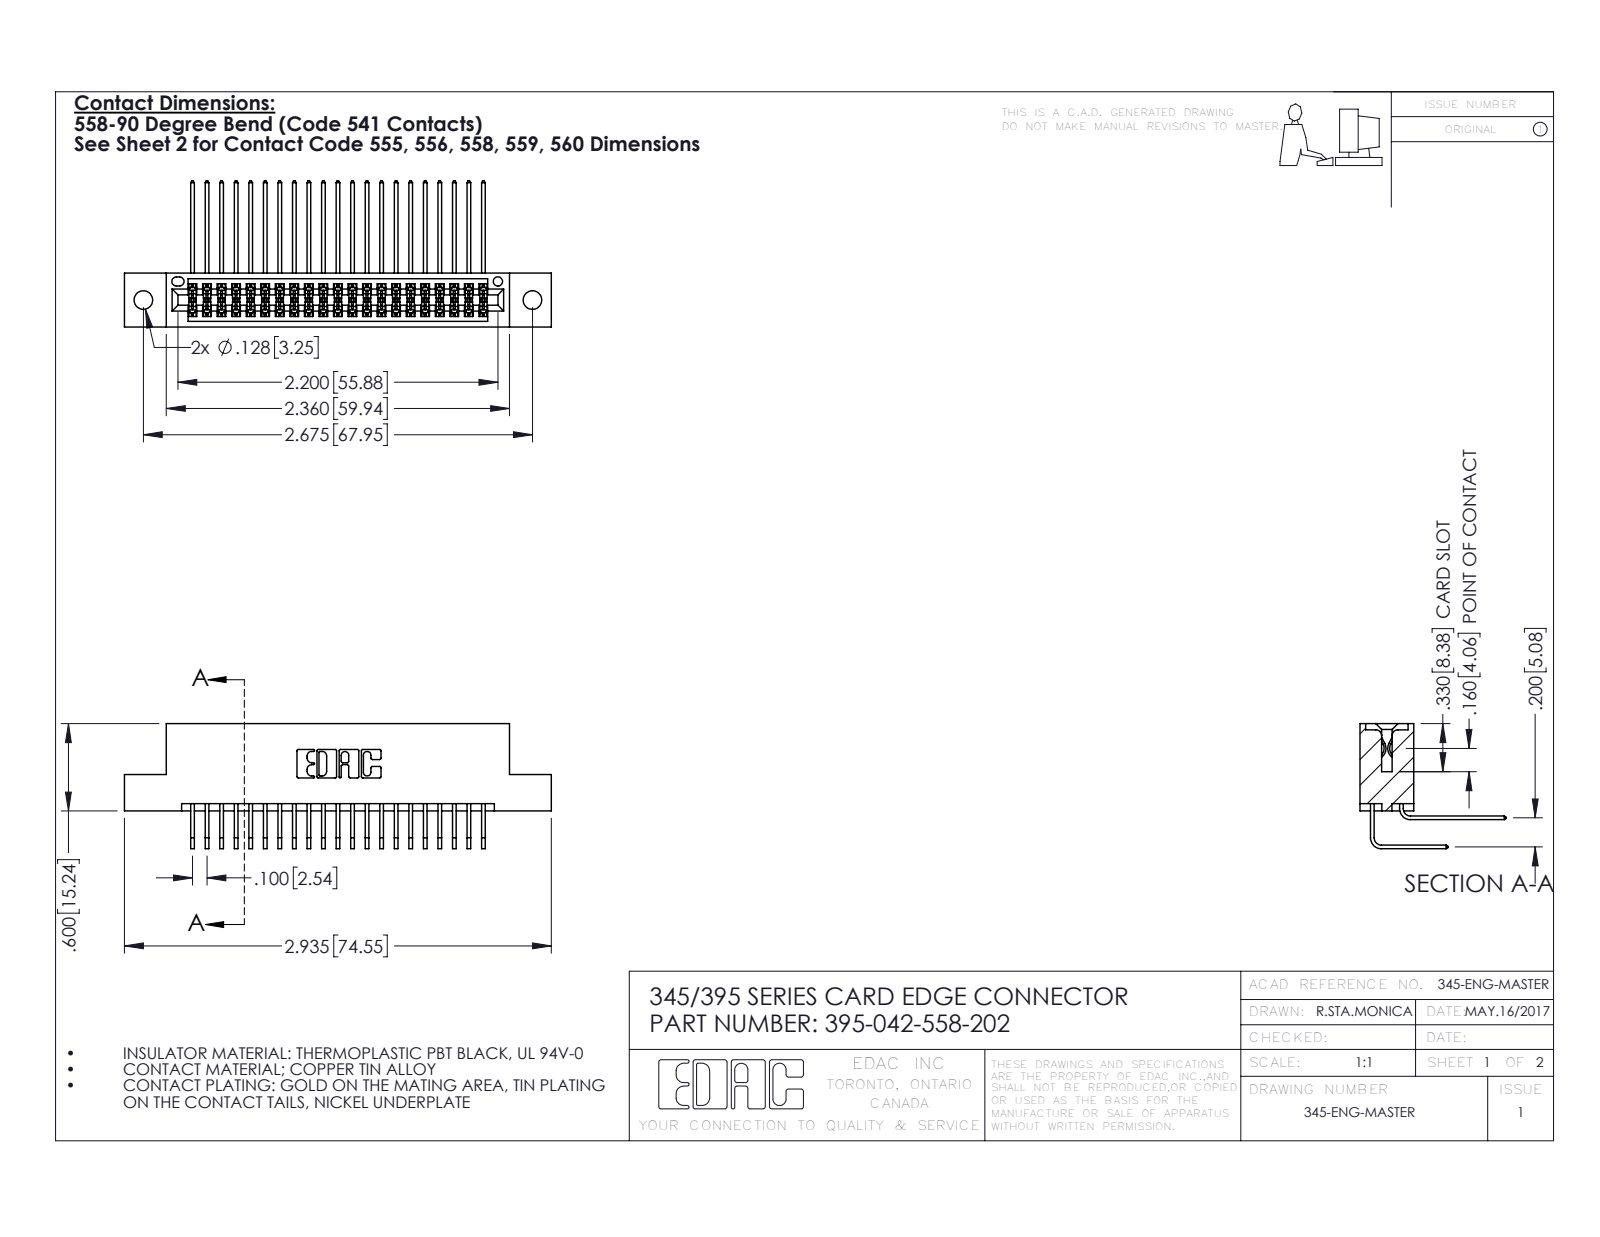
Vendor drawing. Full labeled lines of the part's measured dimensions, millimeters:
Part name (STEP PRODUCT): 345-292-001_558 559 Tail - 1; 345-292-001_558 Tail - 2; 395-042-558-202; 345 Part_Flush Mounting Lugs - 0.128 Dia
STEP written by: SolidWorks 2016 (CONFIG_CONTROL_DESIGN)
Units: millimetres
Bodies: 43 solids, 2310 faces (1550 planar, 760 cylindrical, 0 other)
Overall size (bounding box): 74.5 × 25.5 × 21.8
Volume: 7 260 mm³ · Surface area: 11 180 mm²
Round holes (diameter × count): ⌀3.3 ×2, ⌀1.6 ×1
Partial cylindrical surfaces — rounded edges, fillets, slot ends (radius × count): R0.2 ×64, R0.3 ×22, R0.2 ×6, R0.8 ×6, R0.7 ×3, R0.4 ×2, R0.5 ×2, R0.6 ×2
Main face-to-face distances: 5.1, 1.8, 7.6, 9.4, 2.5, 6.9, 0.6, 5.7, 7.2, 0.6
Hole centre spacings: 6.9, 62, 67.9
